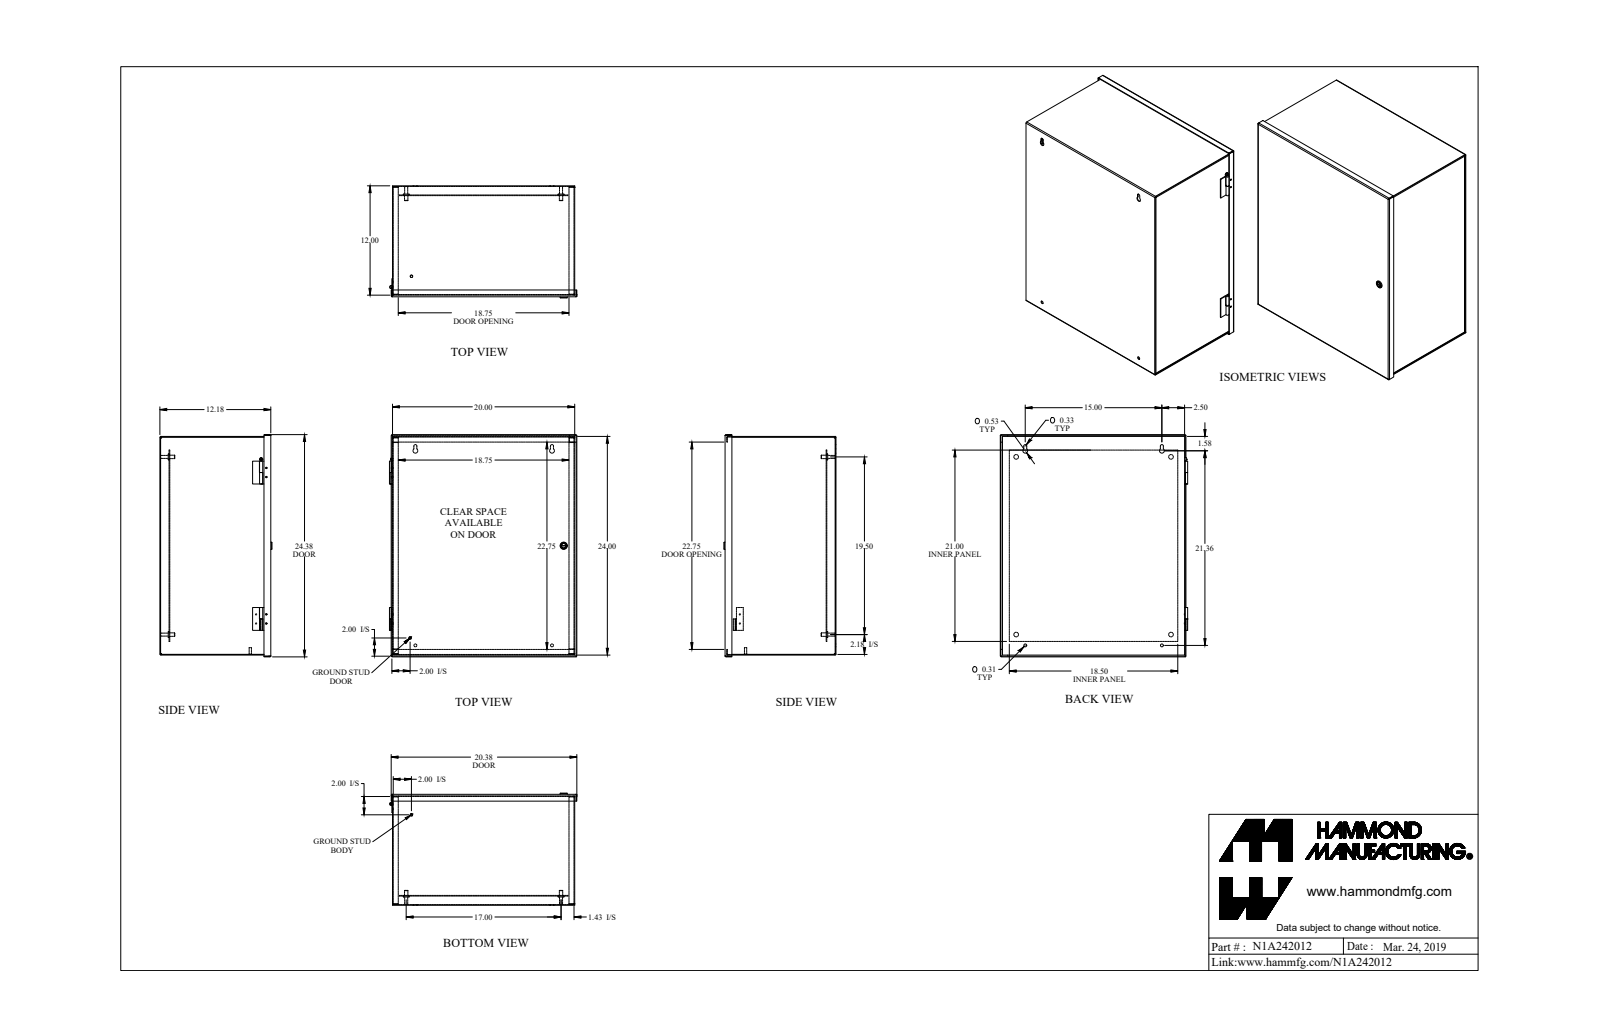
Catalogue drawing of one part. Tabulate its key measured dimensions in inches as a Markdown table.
| quantity | value |
| --- | --- |
| part name | N1A242012 |
| STEP written by | SolidWorks 2018 (AUTOMOTIVE_DESIGN) |
| units | inches |
| bodies | 23 solids, 520 faces (294 planar, 182 cylindrical, 44 other) |
| overall size | 24.384 × 20.574 × 12.299 |
| volume | 186.8 in³ |
| surface area | 5 205 in² |
| round holes (diameter × count) | 0.14 × 8, 0.5 × 4, 0.307 × 2, 0.312 × 2, 0.445 × 2, 0.17 × 1, 0.187 × 1, 0.516 × 1 |
| round bosses / shafts (diameter × count) | 0.128 × 8, 0.375 × 5, 0.65 × 4, 0.33 × 4, 1 × 2, 0.281 × 2, 0.25 × 2, 0.788 × 1 |
| partial cylindrical surfaces (radius × count) | 0.036 × 16, 0.108 × 16, 0.06 × 2, 0.153 × 2, 0.164 × 2, 0.266 × 2, 0.03 × 1, 0.125 × 1 |
| main face-to-face distances | 0.072, 12.105, 1.009, 11.096, 19.928, 12.033, 12.177, 23.928, 1.081, 11.024 |
| hole center spacings | 1, 1.119, 1.553, 2.031, 9.754, 16.044, 16.062, 16.062 |
